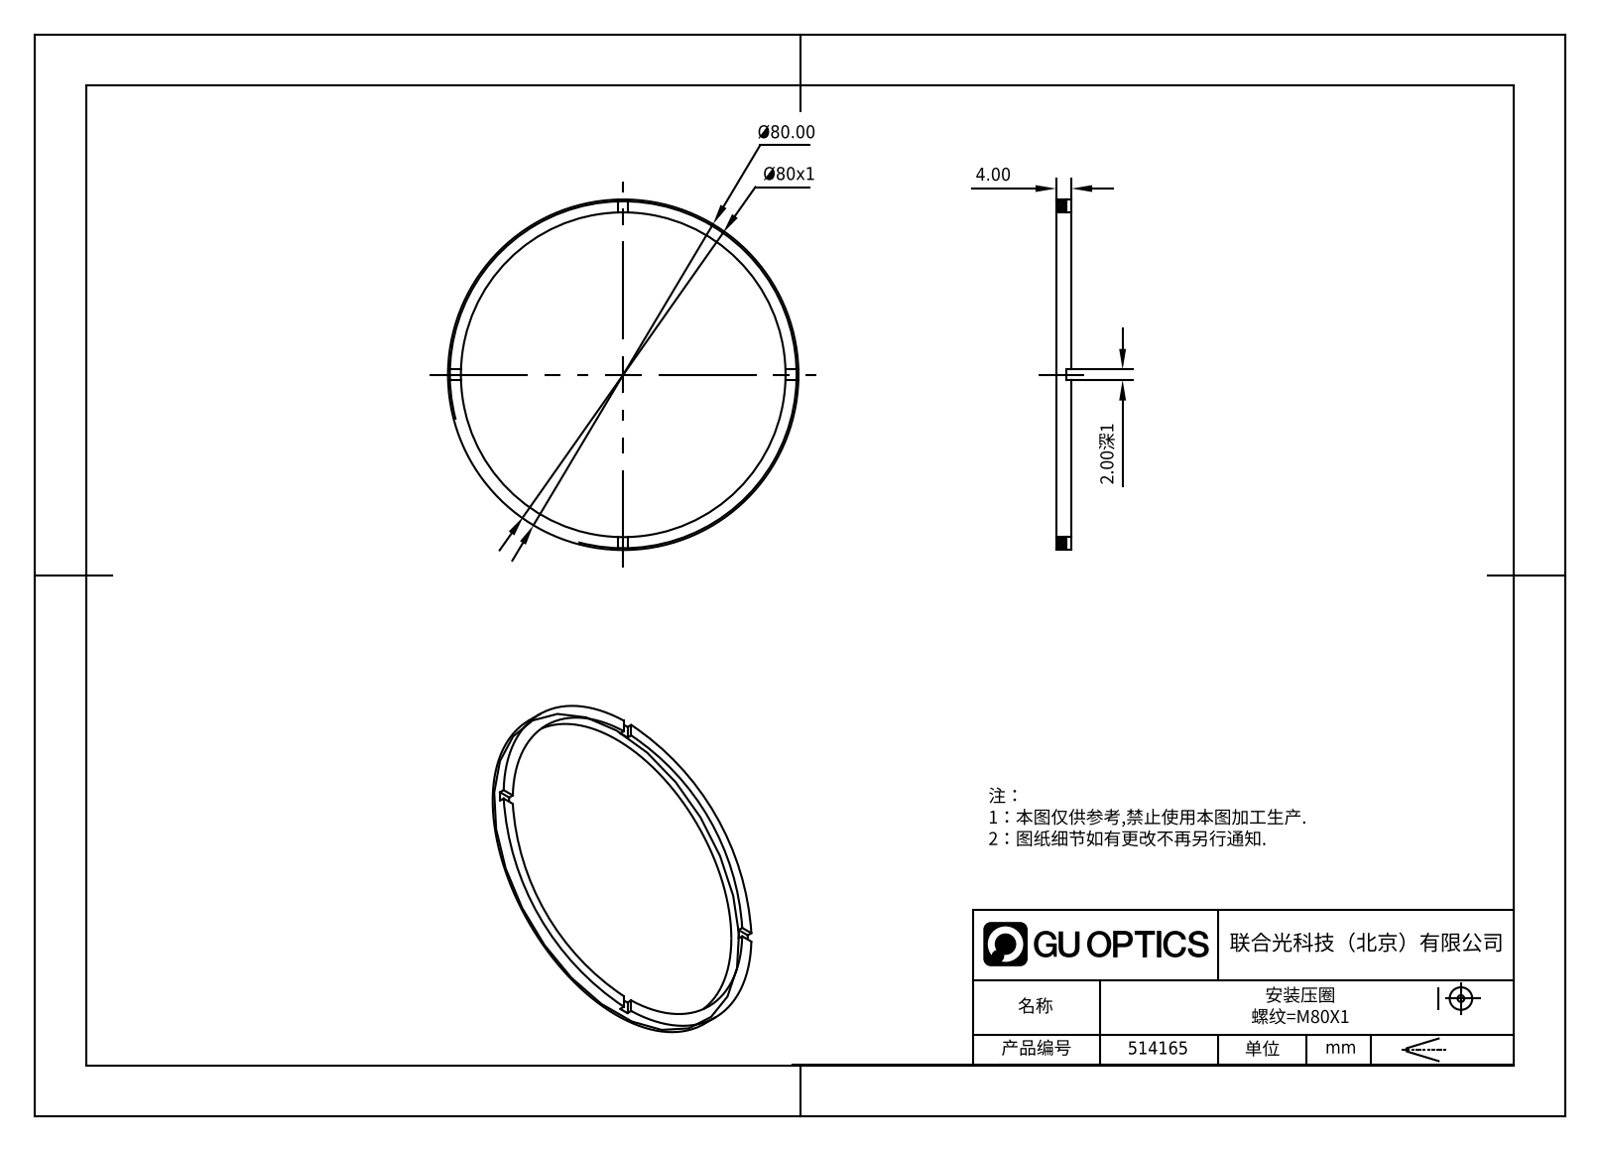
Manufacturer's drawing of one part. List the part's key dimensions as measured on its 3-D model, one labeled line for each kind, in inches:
Part name (STEP PRODUCT): 514165
STEP written by: SolidWorks 2020 (CONFIG_CONTROL_DESIGN)
Units: inches
Bodies: 1 solid, 21 faces (17 planar, 4 cylindrical, 0 other)
Overall size (bounding box): 3.15 × 3.15 × 0.157
Volume: 0.176 in³ · Surface area: 5.262 in²
Round holes (diameter × count): ⌀2.913 ×1
Round bosses / shafts (diameter × count): ⌀3.15 ×1
Main face-to-face distances: 0.157, 0.118, 0.039, 0.079
